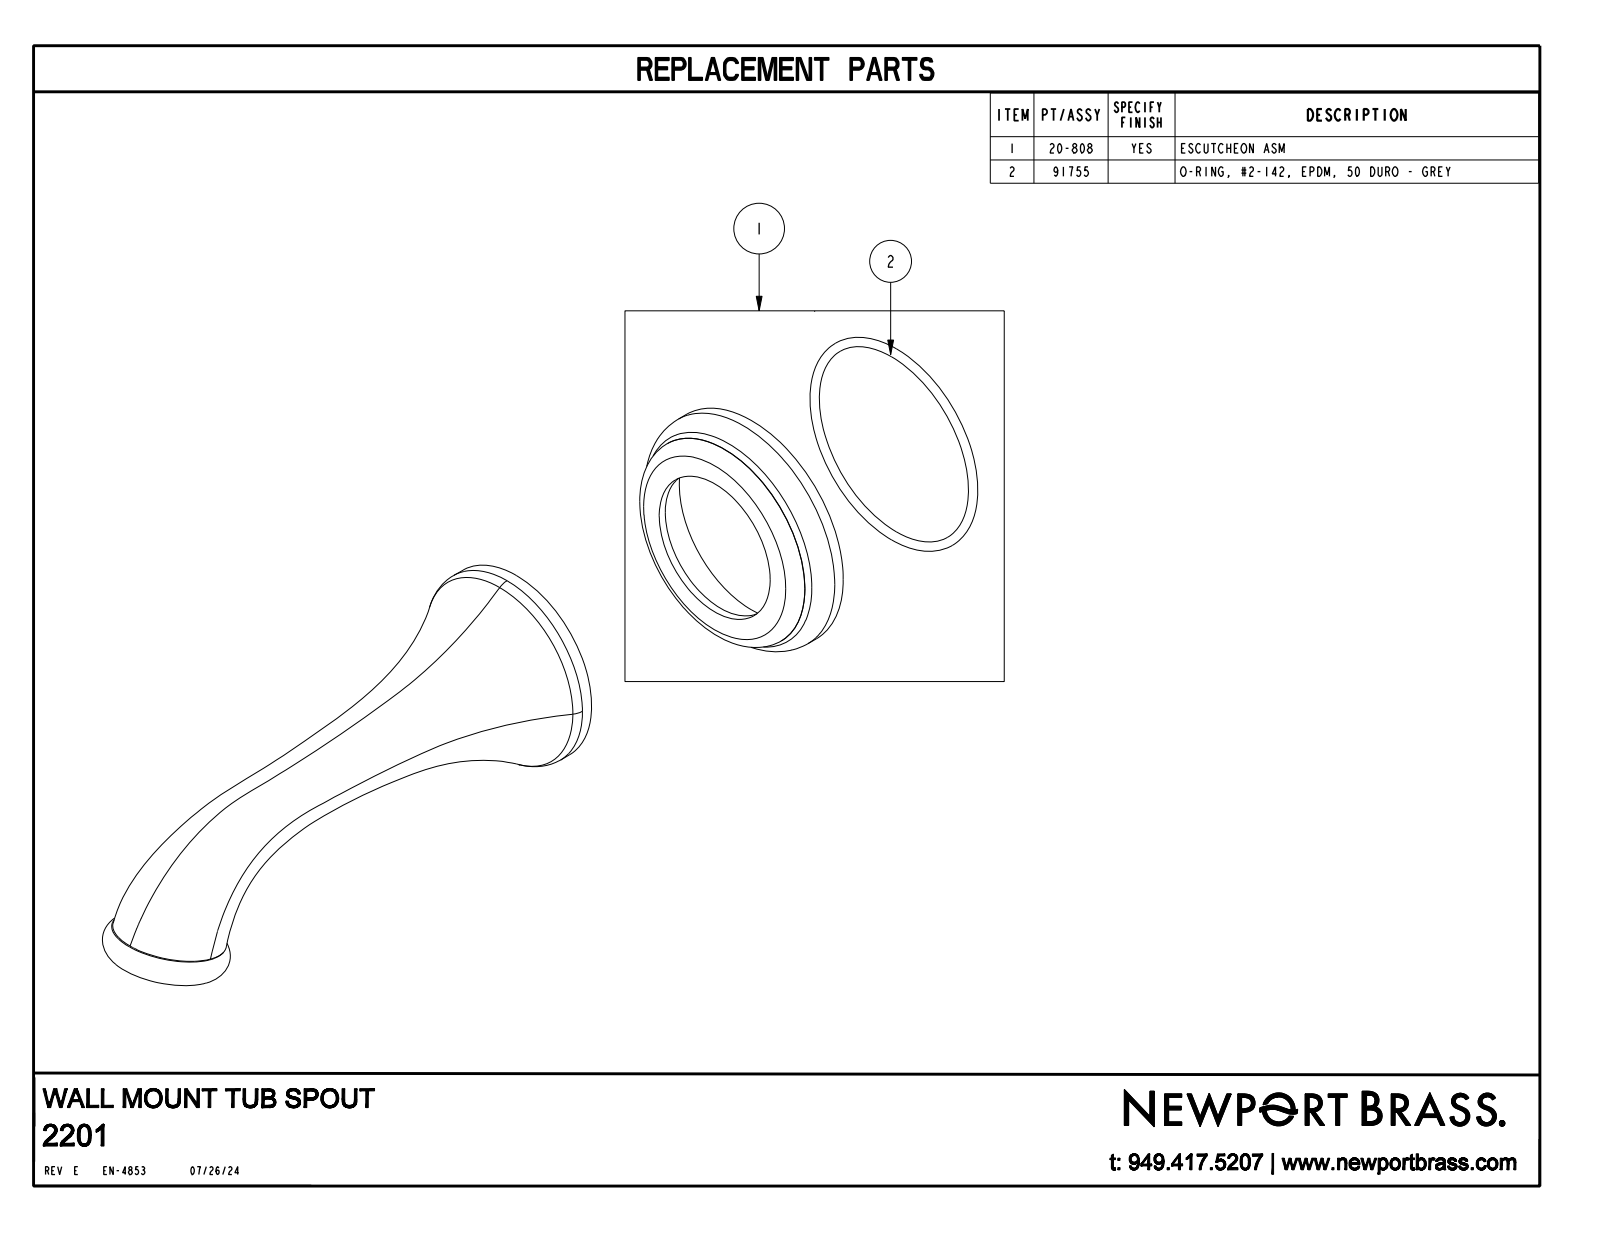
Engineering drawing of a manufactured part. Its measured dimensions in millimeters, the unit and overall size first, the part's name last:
Units: millimetres
Overall size (bounding box): 170.5 × 72.4 × 72.4
Round bosses / shafts (diameter × count): ⌀72.4 ×1, ⌀63.7 ×1, ⌀59.6 ×1, ⌀29.3 ×1
Main face-to-face distances: 14.6, 7.4, 7.5
Volume: 173 200 mm³ · Surface area: 24 460 mm²
Bodies: 1 solid, 29 faces (5 planar, 8 cylindrical, 16 other)
Part name (STEP PRODUCT): 2201
STEP written by: CREO PARAMETRIC BY PTC INC, 2018400 (AUTOMOTIVE_DESIGN)
